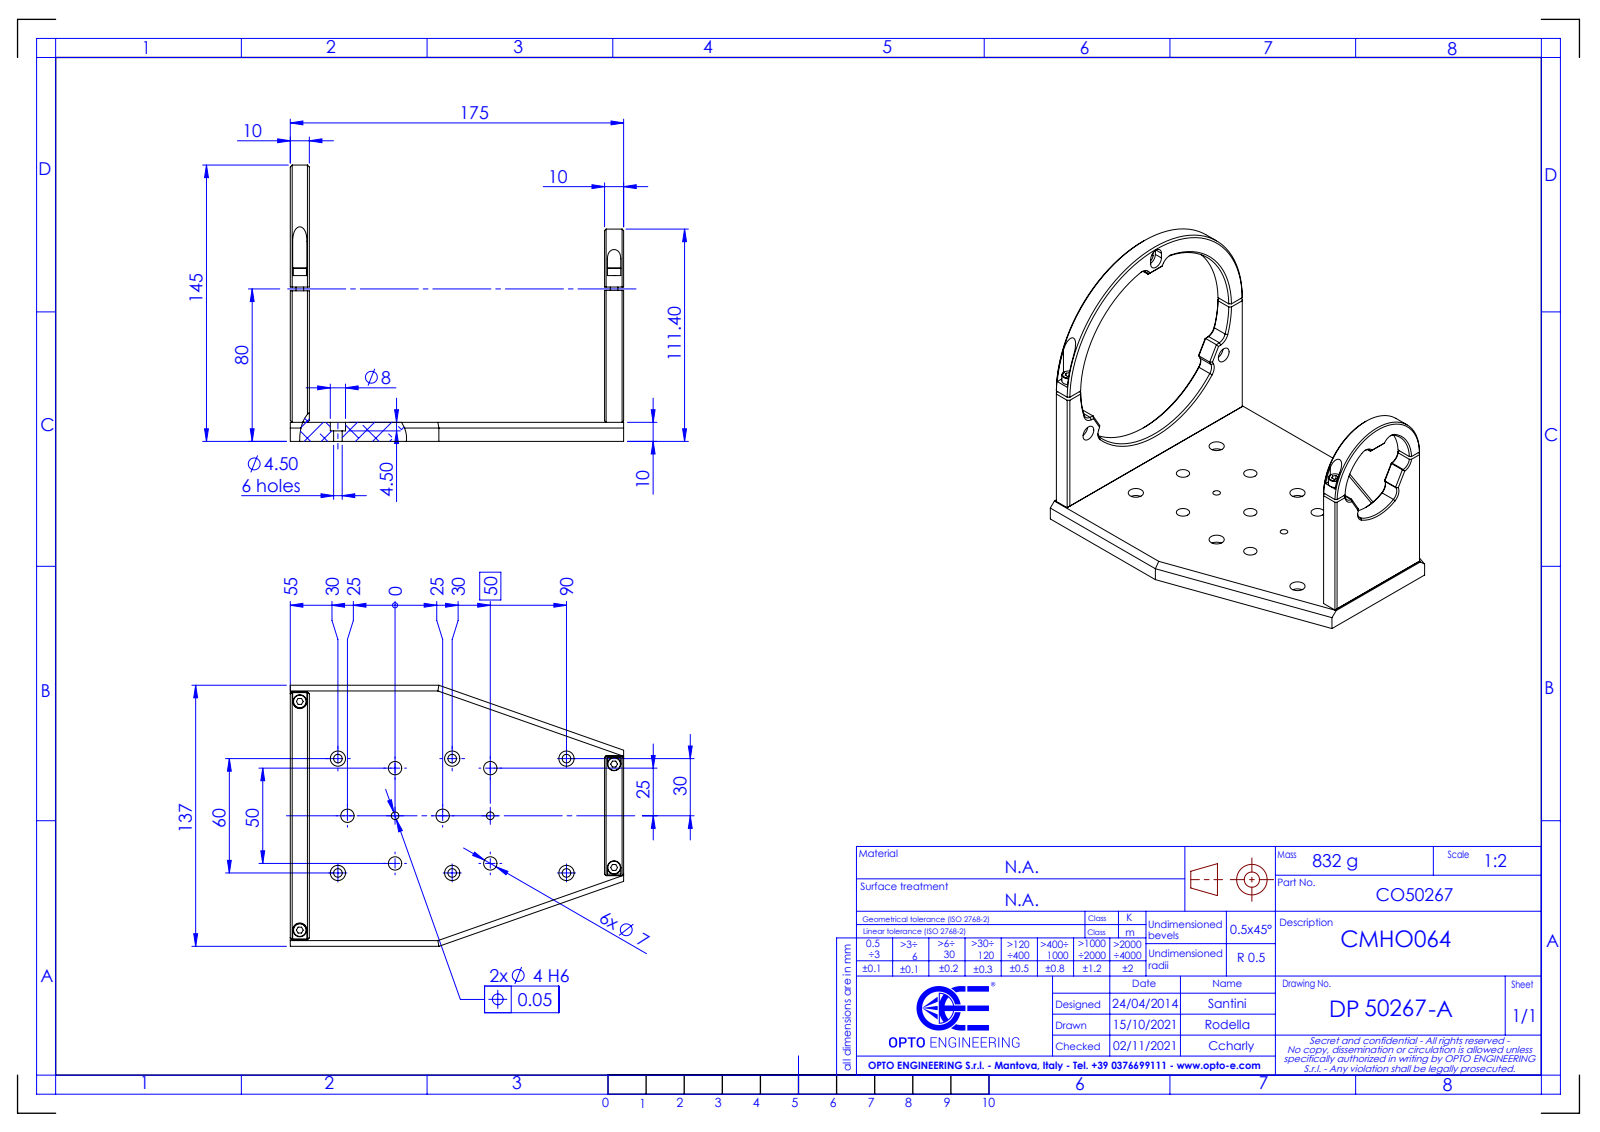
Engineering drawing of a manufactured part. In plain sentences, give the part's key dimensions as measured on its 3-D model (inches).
The part is named "DP50267-A_CMHO064". Its 3-D file was written by "SolidWorks 2021 (CONFIG_CONTROL_DESIGN)". It is 0 solids with 327 faces: 161 planar, 102 cylindrical and 64 other. Overall it measures 6.89 by 5.709 by 5.394 inches. Round holes: 12 of diameter 0.315, 8 of diameter 0.177, 7 of diameter 0.276, 2 of diameter 0.157. Round bosses or shafts: 3 of diameter 0.276, 2 of diameter 0.157. Partial cylindrical surfaces (rounded edges, fillets, slot ends): 12 of radius 0.197, 2 of radius 0.089, 2 of radius 0.148, 2 of radius 0.157, 1 of radius 0.941, 1 of radius 1.236, 1 of radius 2.165, 1 of radius 2.559. The main face-to-face distances are 0.394, 6.496, 6.89, 6.102, 1.323, 3.795, 0.138, 1.461, 3.933, 5.256. The hole center spacings are 1.969, 1.197, 2.201, 2.467, 0.984, 2.362, 1.392, 3.549.
